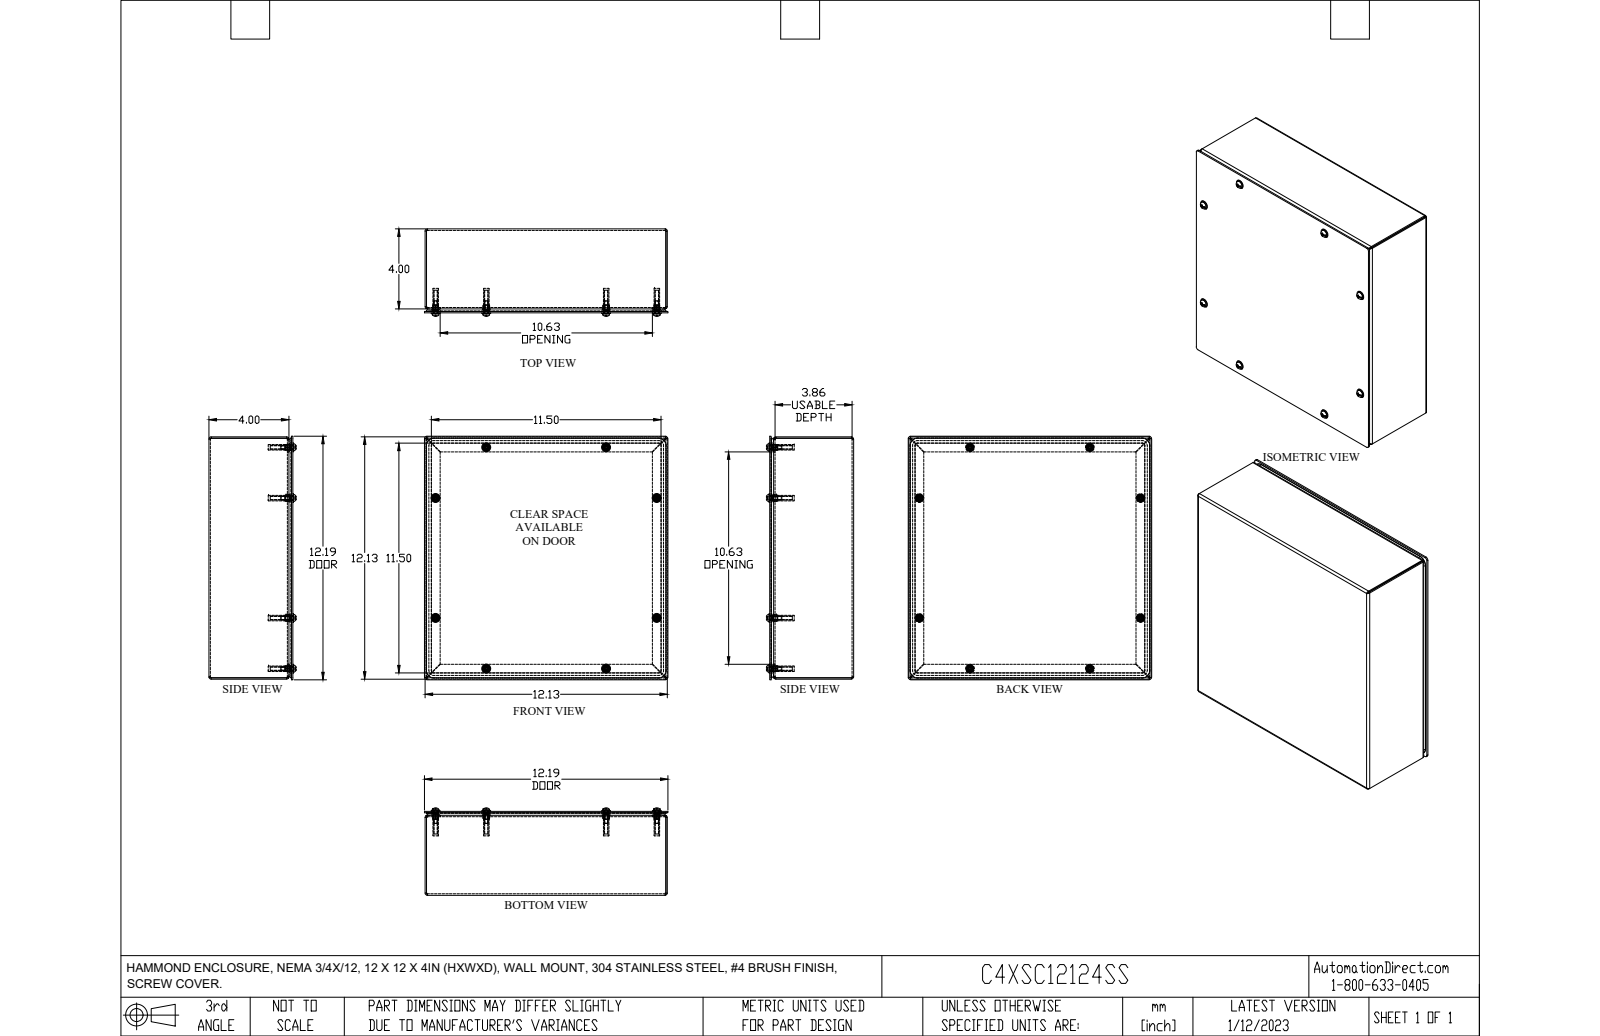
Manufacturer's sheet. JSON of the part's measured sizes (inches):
{"part_name": "C3SC12124GY", "step_written_by": "SolidWorks 2021 (AUTOMOTIVE_DESIGN)", "units": "inches", "bodies": {"solids": 27, "faces": 780, "planar": 480, "cylindrical": 152, "other": 148}, "overall_size": [12.188, 12.188, 4.364], "volume_in3": 37.79, "surface_area_in2": 1108, "round_holes": [[0.159, 8], [0.16, 8], [0.25, 8]], "round_bosses_or_shafts": [[0.44, 8], [0.39, 8], [0.24, 8], [0.19, 8], [0.148, 8], [0.275, 4], [0.275, 4]], "partial_cylinders_radius": [[0.04, 8], [0.11, 8], [0.125, 8], [0.16, 8], [0.126, 4], [0.374, 4]], "face_to_face_distances": [0.07, 0.072, 4.127, 4.055, 4.197, 4.125, 12.13, 12.06, 0.07, 11.99], "hole_center_spacings": [8.906, 3.589, 6, 11.075, 12.074, 12.596]}
